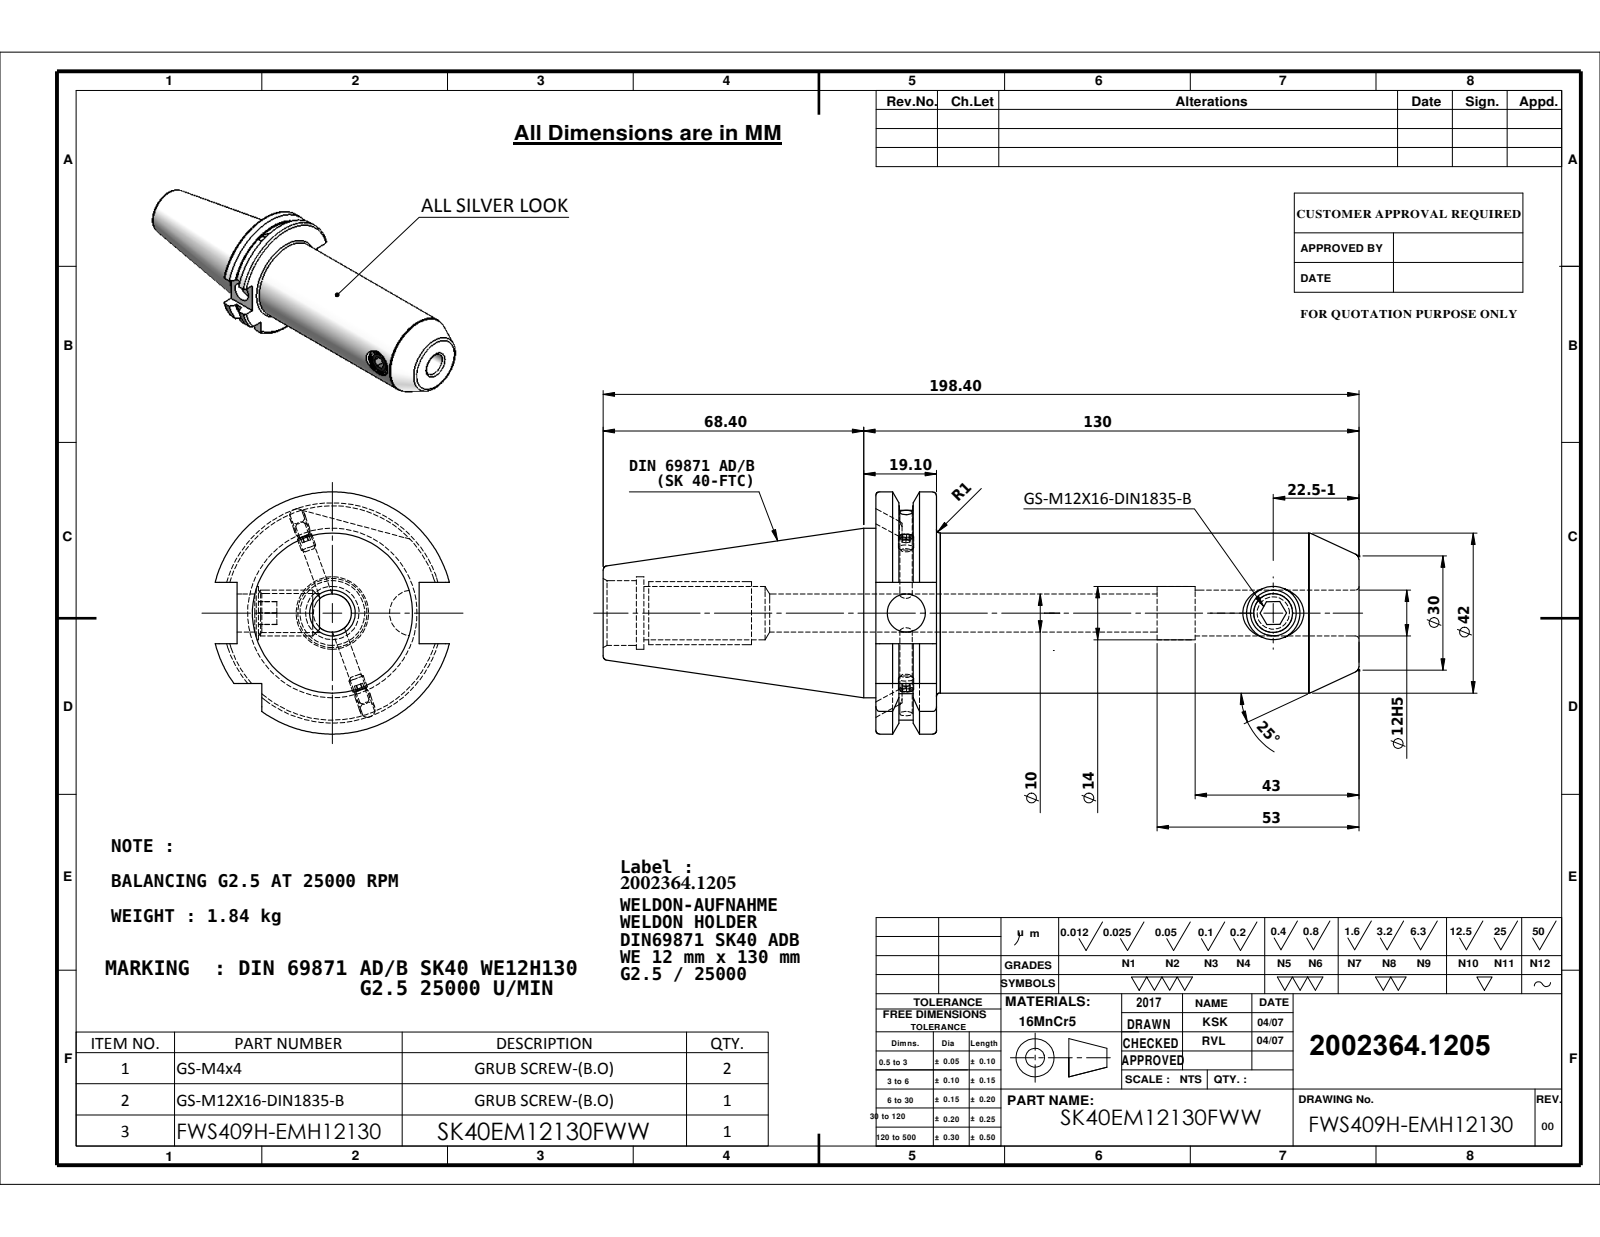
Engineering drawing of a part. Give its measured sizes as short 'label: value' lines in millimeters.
name: M12X16._ISO 4026 - M12 x 12-N; SK40EM12130FWW; 91406-WE712130; M4X4_DIN 913 - M4 x 4-N
written by: SolidWorks 2009 (CONFIG_CONTROL_DESIGN)
unit: mm
bodies: 4 solids, 158 faces (58 planar, 44 cylindrical, 56 other)
size: 198.4 × 63.55 × 61.48
volume: 239 596 mm³; area: 40 029 mm²
holes: 2× ⌀10, 2× ⌀14, 1× ⌀3.3, 1× ⌀10.2, 1× ⌀12, 1× ⌀17, 1× ⌀19
bosses: 2× ⌀4, 1× ⌀44.45, 1× ⌀42, 1× ⌀12
rounds: 1× R28.12, 1× R31.77
face distances: 15.9, 126.8, 110.9, 16.1, 47.8, 71.6, 87.5, 198.4, 10.7, 60.9
hole spacings: 96.35
